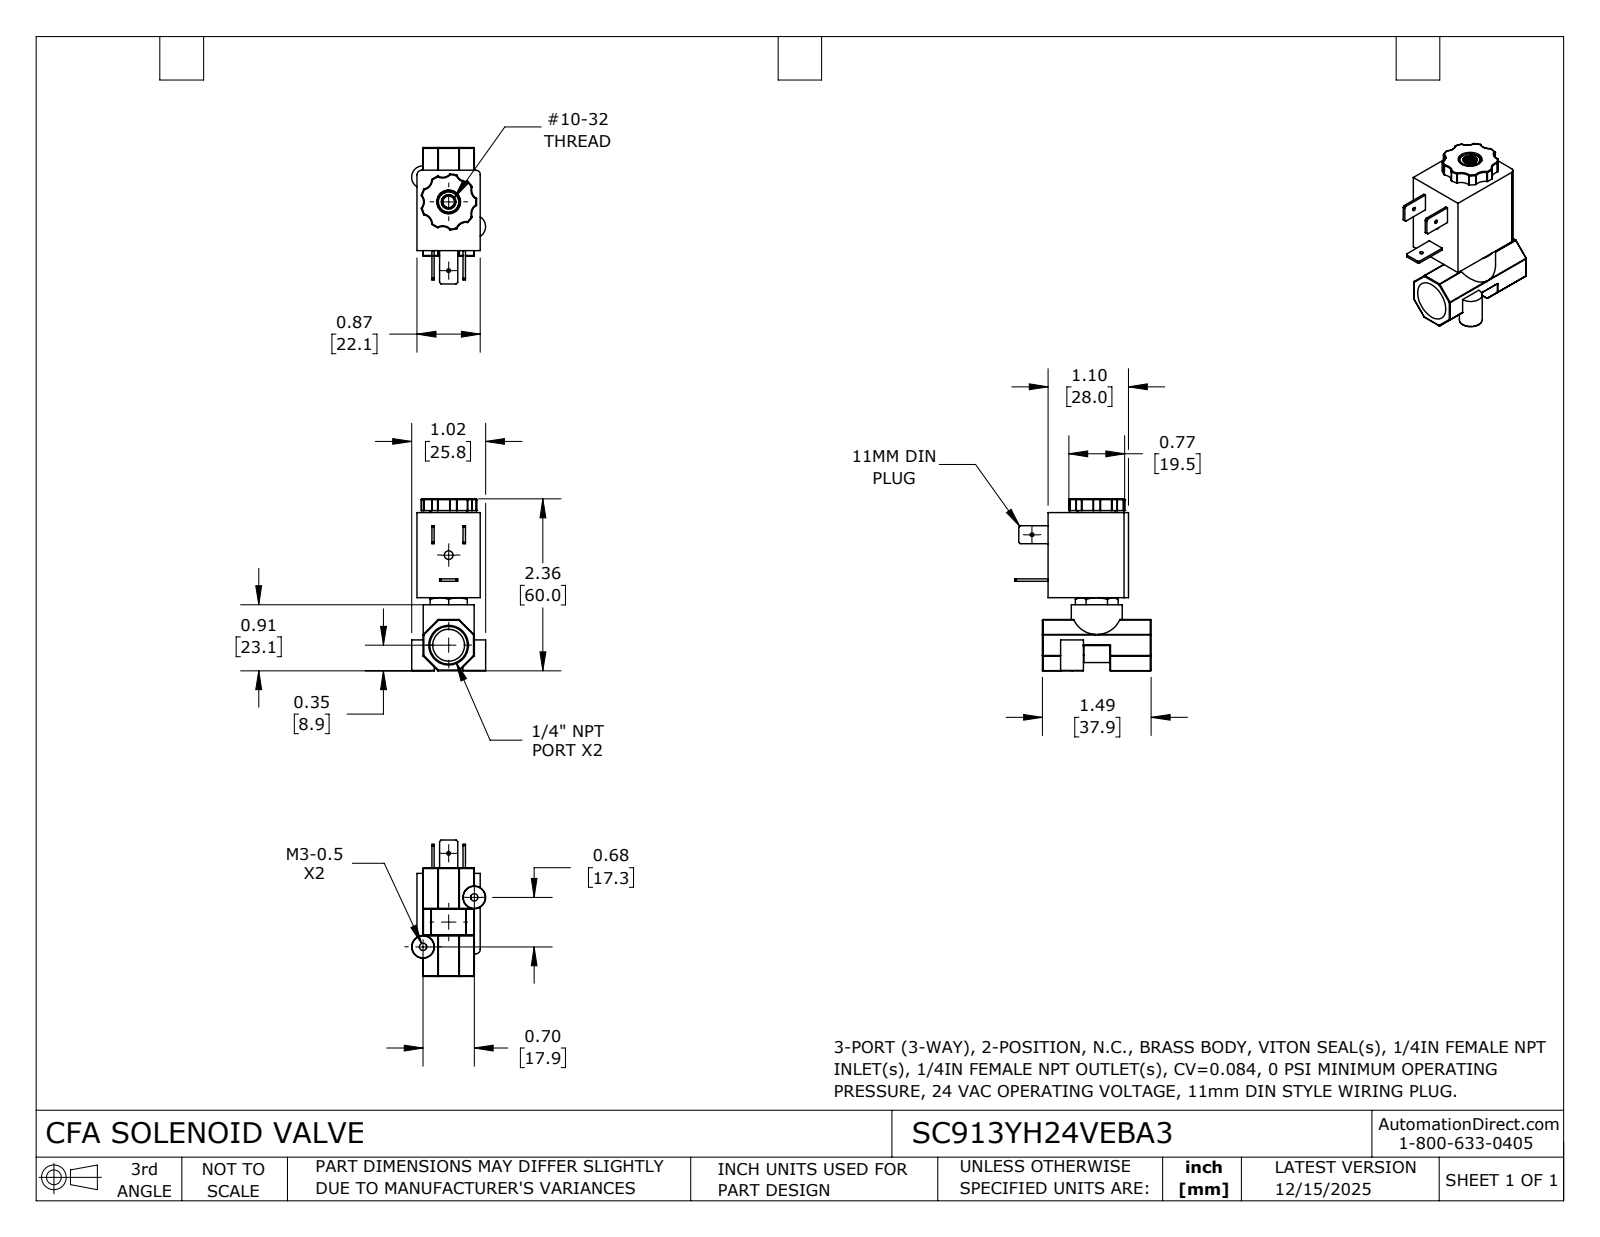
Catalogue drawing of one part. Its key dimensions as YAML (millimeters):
part_name: "SC913YH24VEBA3"
step_written_by: "SolidWorks 2024 (CONFIG_CONTROL_DESIGN)"
units: millimeters
bodies: {solids: 1, faces: 308, planar: 68, cylindrical: 139, other: 101}
overall_size: [60, 47.6, 25.8]
volume: 27280
surface_area: 10390
round_holes:
  - {diameter: 1.3, count: 2}
  - {diameter: 2.5, count: 2}
  - {diameter: 3, count: 1}
  - {diameter: 4.1, count: 1}
  - {diameter: 8.3, count: 1}
  - {diameter: 11.1, count: 1}
round_bosses_or_shafts:
  - {diameter: 8, count: 2}
  - {diameter: 17.8, count: 1}
  - {diameter: 8, count: 1}
partial_cylinders:
  - {radius: 0.3, count: 42}
  - {radius: 0.1, count: 14}
  - {radius: 3.4, count: 7}
  - {radius: 1.5, count: 2}
  - {radius: 3.4, count: 2}
  - {radius: 6, count: 1}
  - {radius: 7.8, count: 1}
  - {radius: 9.8, count: 1}
face_to_face_distances: [22.1, 17.9, 28, 29.6, 2.1, 20, 25.6, 55.2, 60, 34.5]
hole_center_spacings: [12.4, 17.8, 24, 24.9, 31.4, 33.9]
